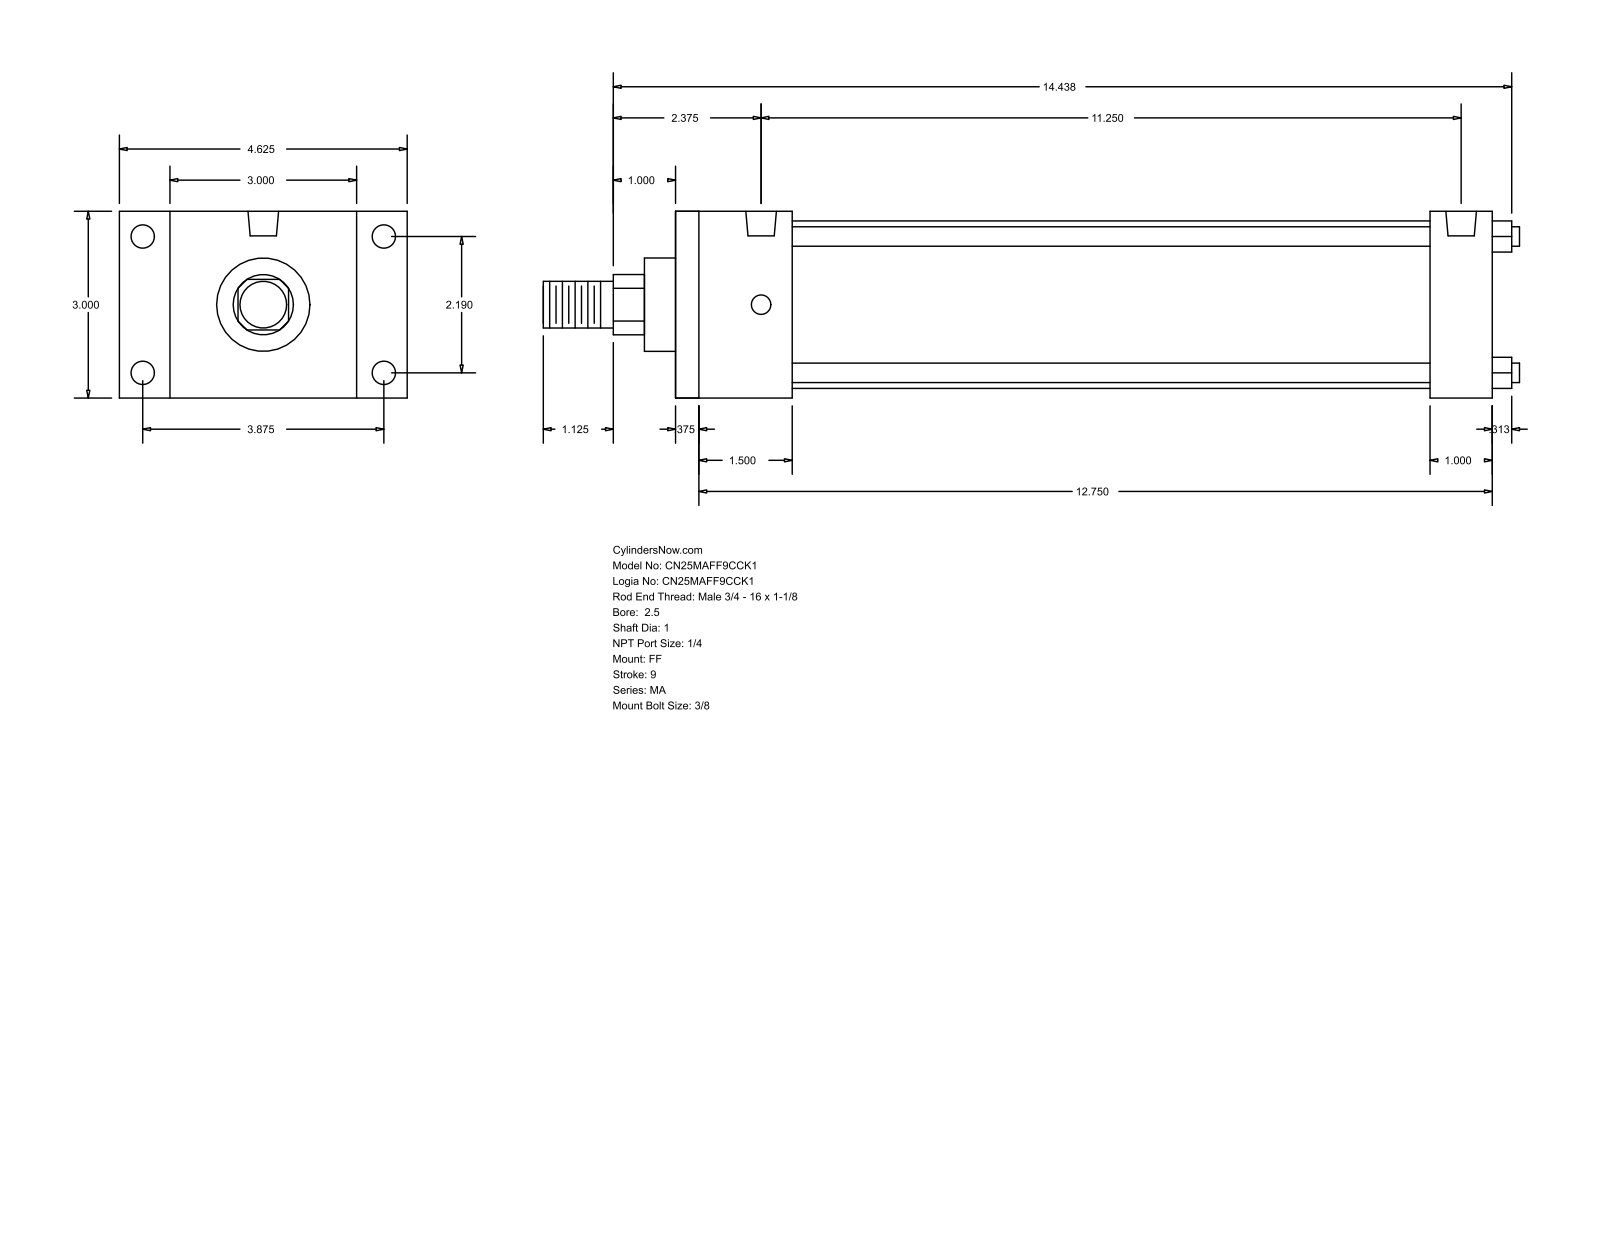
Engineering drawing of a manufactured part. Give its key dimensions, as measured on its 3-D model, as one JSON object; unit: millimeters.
{"part_name": "MA_FF__0250_1", "step_written_by": "GSSL Pune (CONFIG_CONTROL_DESIGN)", "units": "millimeters", "bodies": {"solids": 0, "faces": 92, "planar": 64, "cylindrical": 28, "other": 0}, "overall_size": [398.46, 117.47, 76.2], "round_holes": [[7.94, 4], [9.53, 4], [12.49, 2]], "round_bosses_or_shafts": [[7.94, 4], [68.33, 1], [38.1, 1], [25.4, 1], [19.05, 1]], "partial_cylinders_radius": [[12.29, 1]], "face_to_face_distances": [76.2, 333.37, 323.85, 9.52, 25.39, 47.63, 307.98, 38.11, 298.46, 260.35], "hole_center_spacings": [55.62, 98.42, 113.05, 285.74]}
